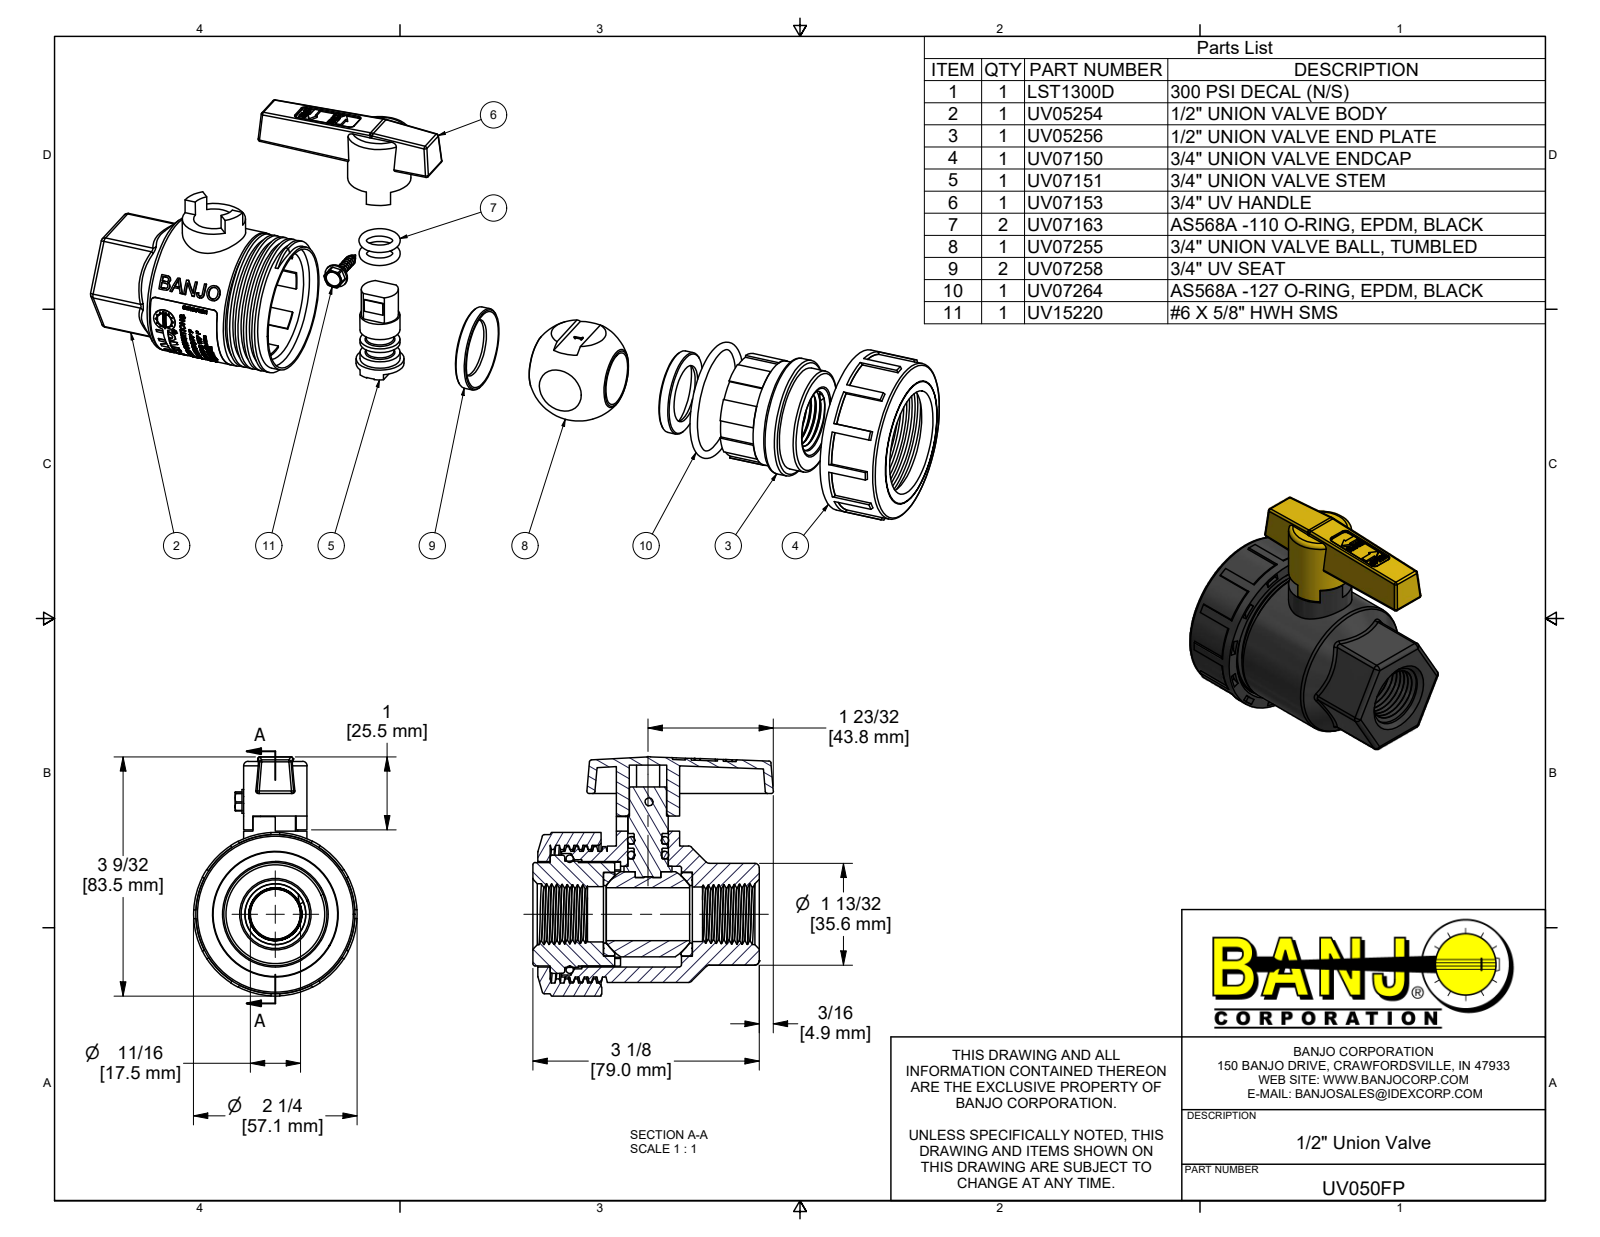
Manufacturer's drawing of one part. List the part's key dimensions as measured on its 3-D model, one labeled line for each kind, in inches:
Part name (STEP PRODUCT): UV050FP; UV05254; uv05254; UVL1000-D1.875 (+8 more)
STEP written by: Autodesk Inventor 2019 (AUTOMOTIVE_DESIGN)
Units: inches
Bodies: 13 solids, 2352 faces (1182 planar, 373 cylindrical, 797 other)
Overall size (bounding box): 13.633 × 3.287 × 2.25
Volume: 7.265 in³ · Surface area: 159.7 in²
Round holes (diameter × count): ⌀0.515 ×1, ⌀0.558 ×1, ⌀0.727 ×1, ⌀0.75 ×1, ⌀0.76 ×1, ⌀0.79 ×1, ⌀1.153 ×1, ⌀1.157 ×1, ⌀1.45 ×1, ⌀1.5 ×1, ⌀1.67 ×1, ⌀1.778 ×1
Round bosses / shafts (diameter × count): ⌀2.25 ×1, ⌀2.187 ×1, ⌀1.875 ×1, ⌀1.86 ×1, ⌀1.726 ×1, ⌀1.625 ×1, ⌀1.46 ×1, ⌀1.42 ×1
Partial cylindrical surfaces — rounded edges, fillets, slot ends (radius × count): R0.03 ×23, R0.06 ×16, R0.01 ×4, R0.05 ×4, R0.5 ×3, R0.139 ×1, R0.255 ×1, R0.263 ×1
Main face-to-face distances: 0.11, 0.731, 1.955, 1.224, 0.7, 1.4, 0.031, 1.255, 0.919, 0.969
